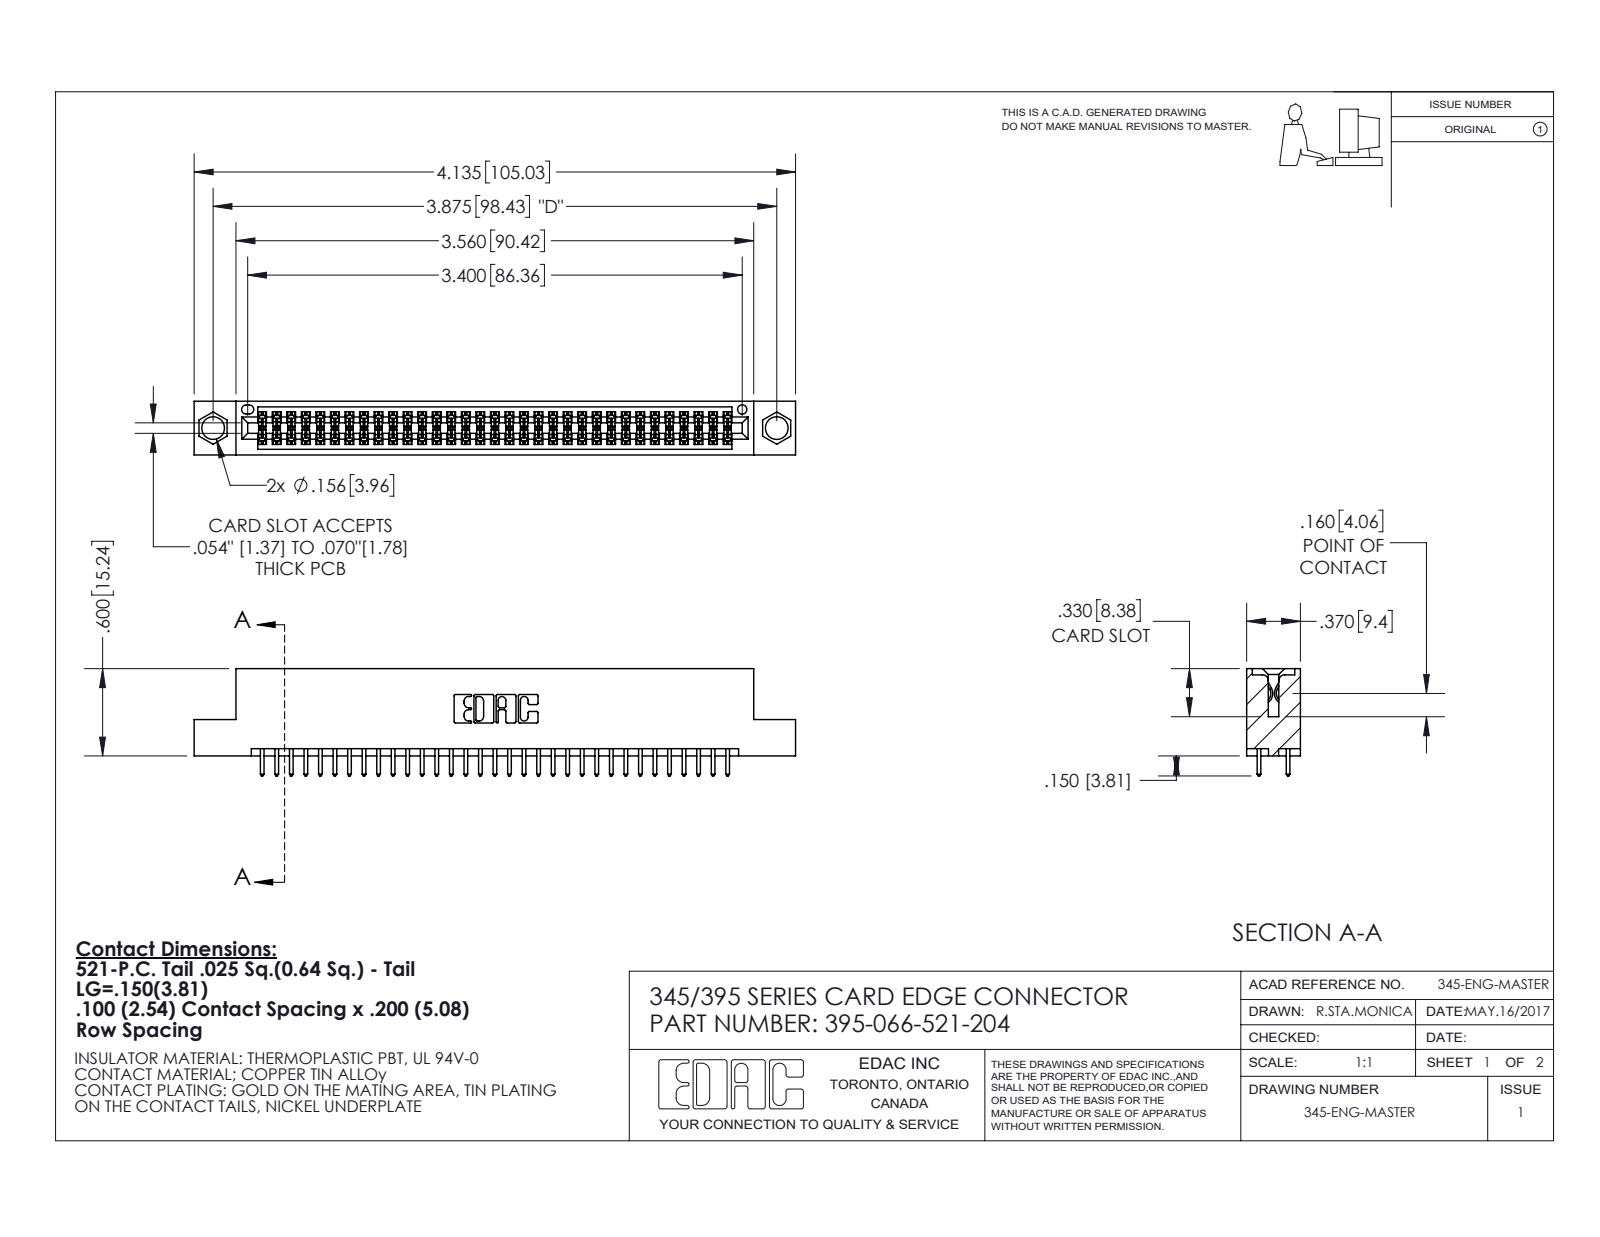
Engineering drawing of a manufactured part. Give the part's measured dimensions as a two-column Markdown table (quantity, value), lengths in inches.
| quantity | value |
| --- | --- |
| part name | 345 Part_Flush Mounting Lugs - 0.156 Dia-TI; 395-066-521-204; 345-292-001_345-293-121 |
| STEP written by | SolidWorks 2020 (CONFIG_CONTROL_DESIGN) |
| units | inches |
| bodies | 67 solids, 3440 faces (2272 planar, 1168 cylindrical, 0 other) |
| overall size | 4.135 × 0.737 × 0.37 |
| volume | 0.609 in³ |
| surface area | 22.11 in² |
| round holes (diameter × count) | 0.156 × 2, 0.064 × 1 |
| partial cylindrical surfaces (radius × count) | 0.006 × 132, 0.01 × 66, 0.01 × 22, 0.007 × 6, 0.031 × 6, 0.026 × 3, 0.014 × 2, 0.019 × 2 |
| main face-to-face distances | 0.072, 0.298, 0.2, 0.37, 0.098, 0.272, 0.025, 0.225, 0.175, 0.149 |
| hole center spacings | 0.27, 3.64, 3.875 |
